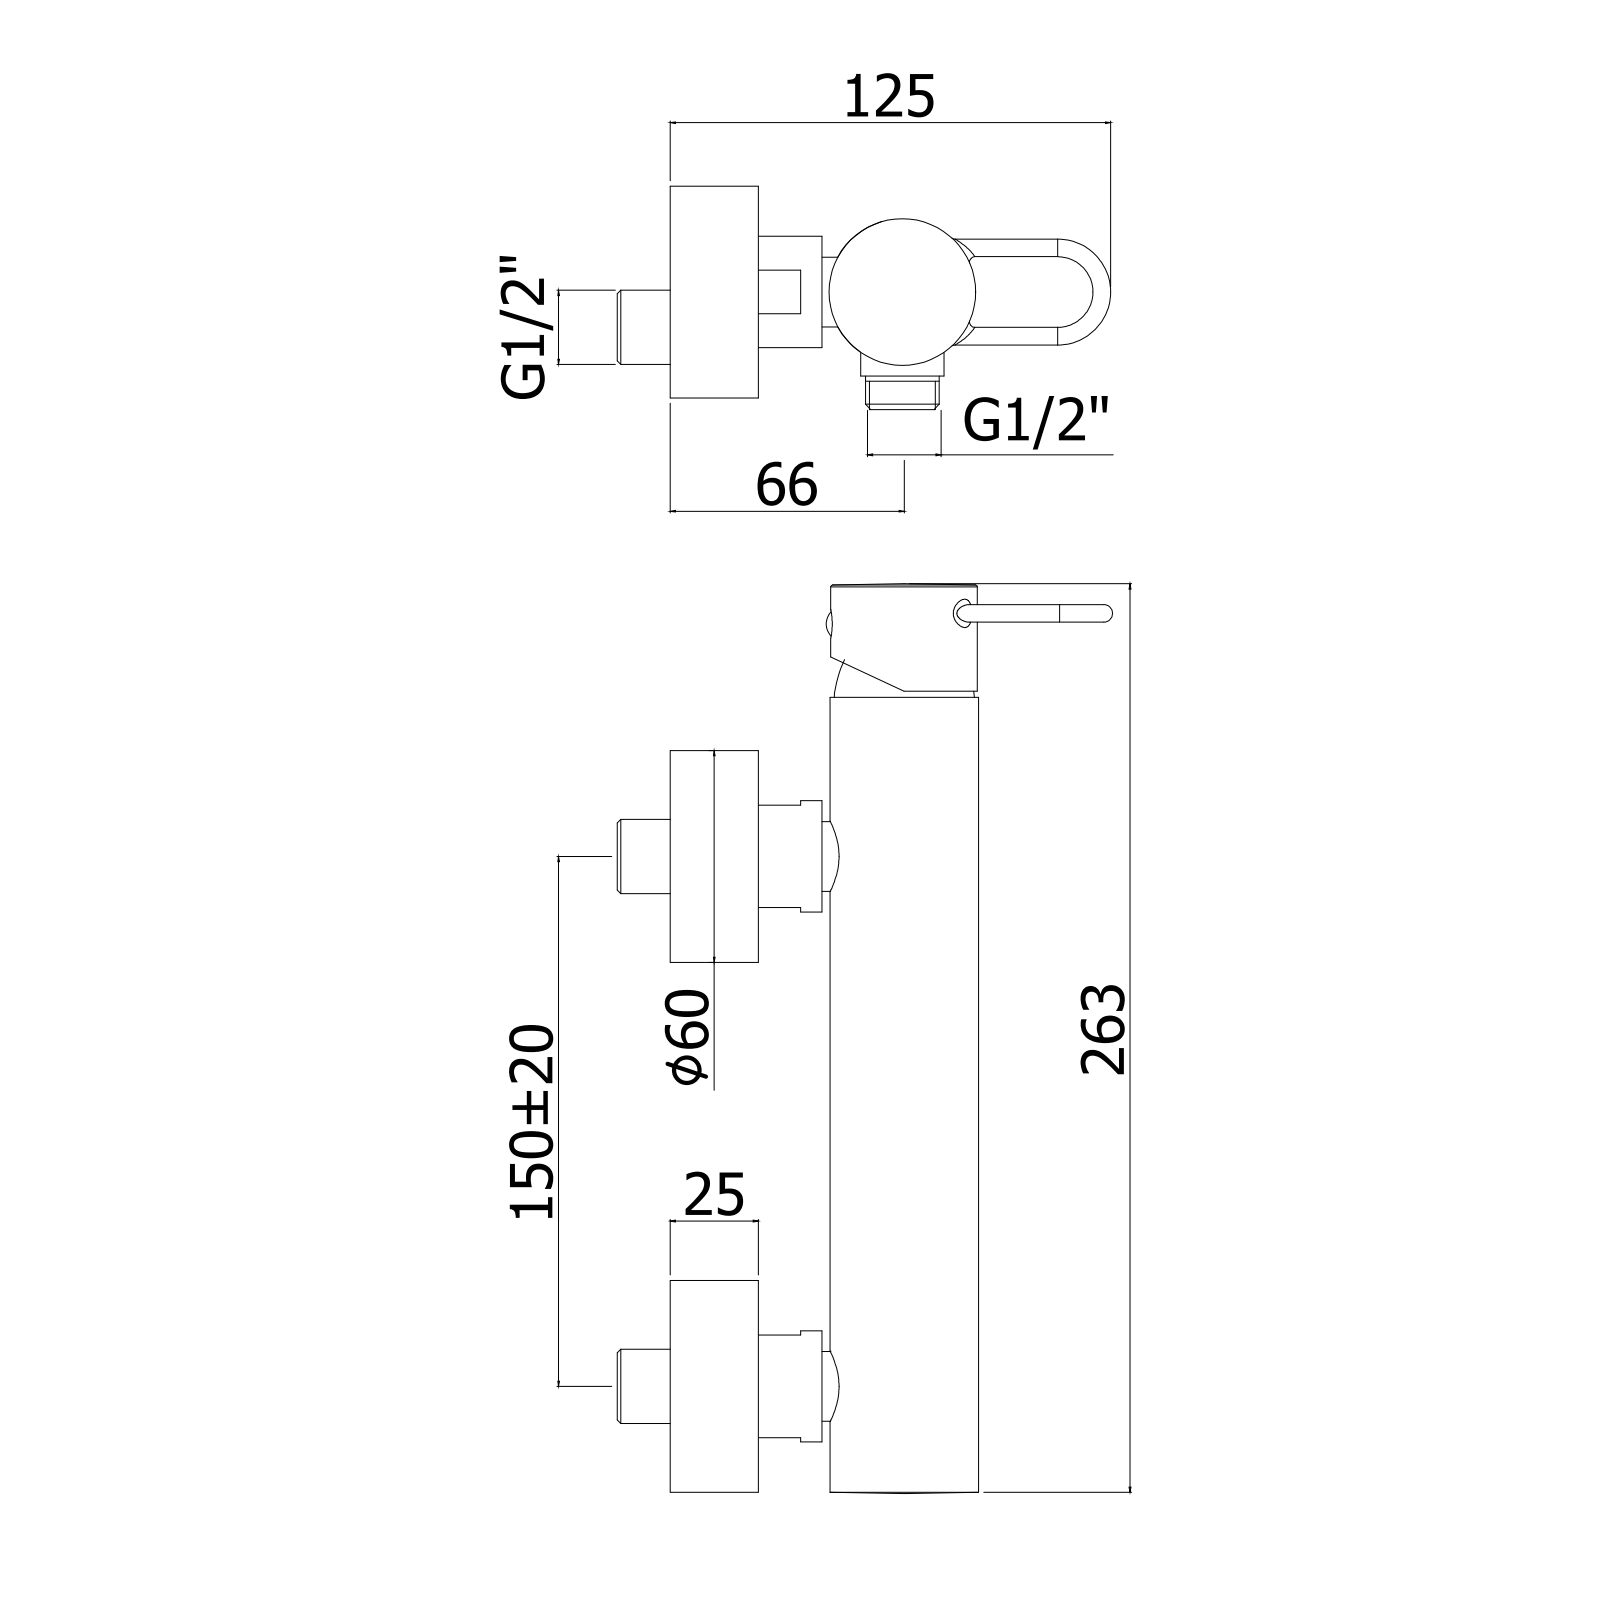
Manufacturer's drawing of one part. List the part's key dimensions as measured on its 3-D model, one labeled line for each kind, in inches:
Part name (STEP PRODUCT): JK168CR
STEP written by: CREO PARAMETRIC BY PTC INC, 2020044 (CONFIG_CONTROL_DESIGN)
Units: inches
Bodies: 2 solids, 236 faces (76 planar, 93 cylindrical, 67 other)
Overall size (bounding box): 10.591 × 4.909 × 2.484
Volume: 26.58 in³ · Surface area: 135.8 in²
Round holes (diameter × count): ⌀0.295 ×6, ⌀0.657 ×3, ⌀0.197 ×2, ⌀0.413 ×2, ⌀0.787 ×2, ⌀0.118 ×1, ⌀0.165 ×1, ⌀0.217 ×1, ⌀0.531 ×1, ⌀0.591 ×1, ⌀1.205 ×1, ⌀1.339 ×1
Round bosses / shafts (diameter × count): ⌀2.35 ×2, ⌀1.634 ×2, ⌀1.24 ×2, ⌀0.776 ×2, ⌀0.197 ×2, ⌀0.925 ×1, ⌀0.823 ×1
Partial cylindrical surfaces — rounded edges, fillets, slot ends (radius × count): R0.061 ×2, R0.207 ×1, R0.354 ×1, R0.813 ×1
Main face-to-face distances: 0.984, 0.709, 1.693, 2.906, 2.283, 1.299, 0.591, 5.906, 1.142, 0.374
Hole centre spacings: 0.333, 0.426, 0.53, 0.586, 0.857, 0.972, 0.512, 0.551
